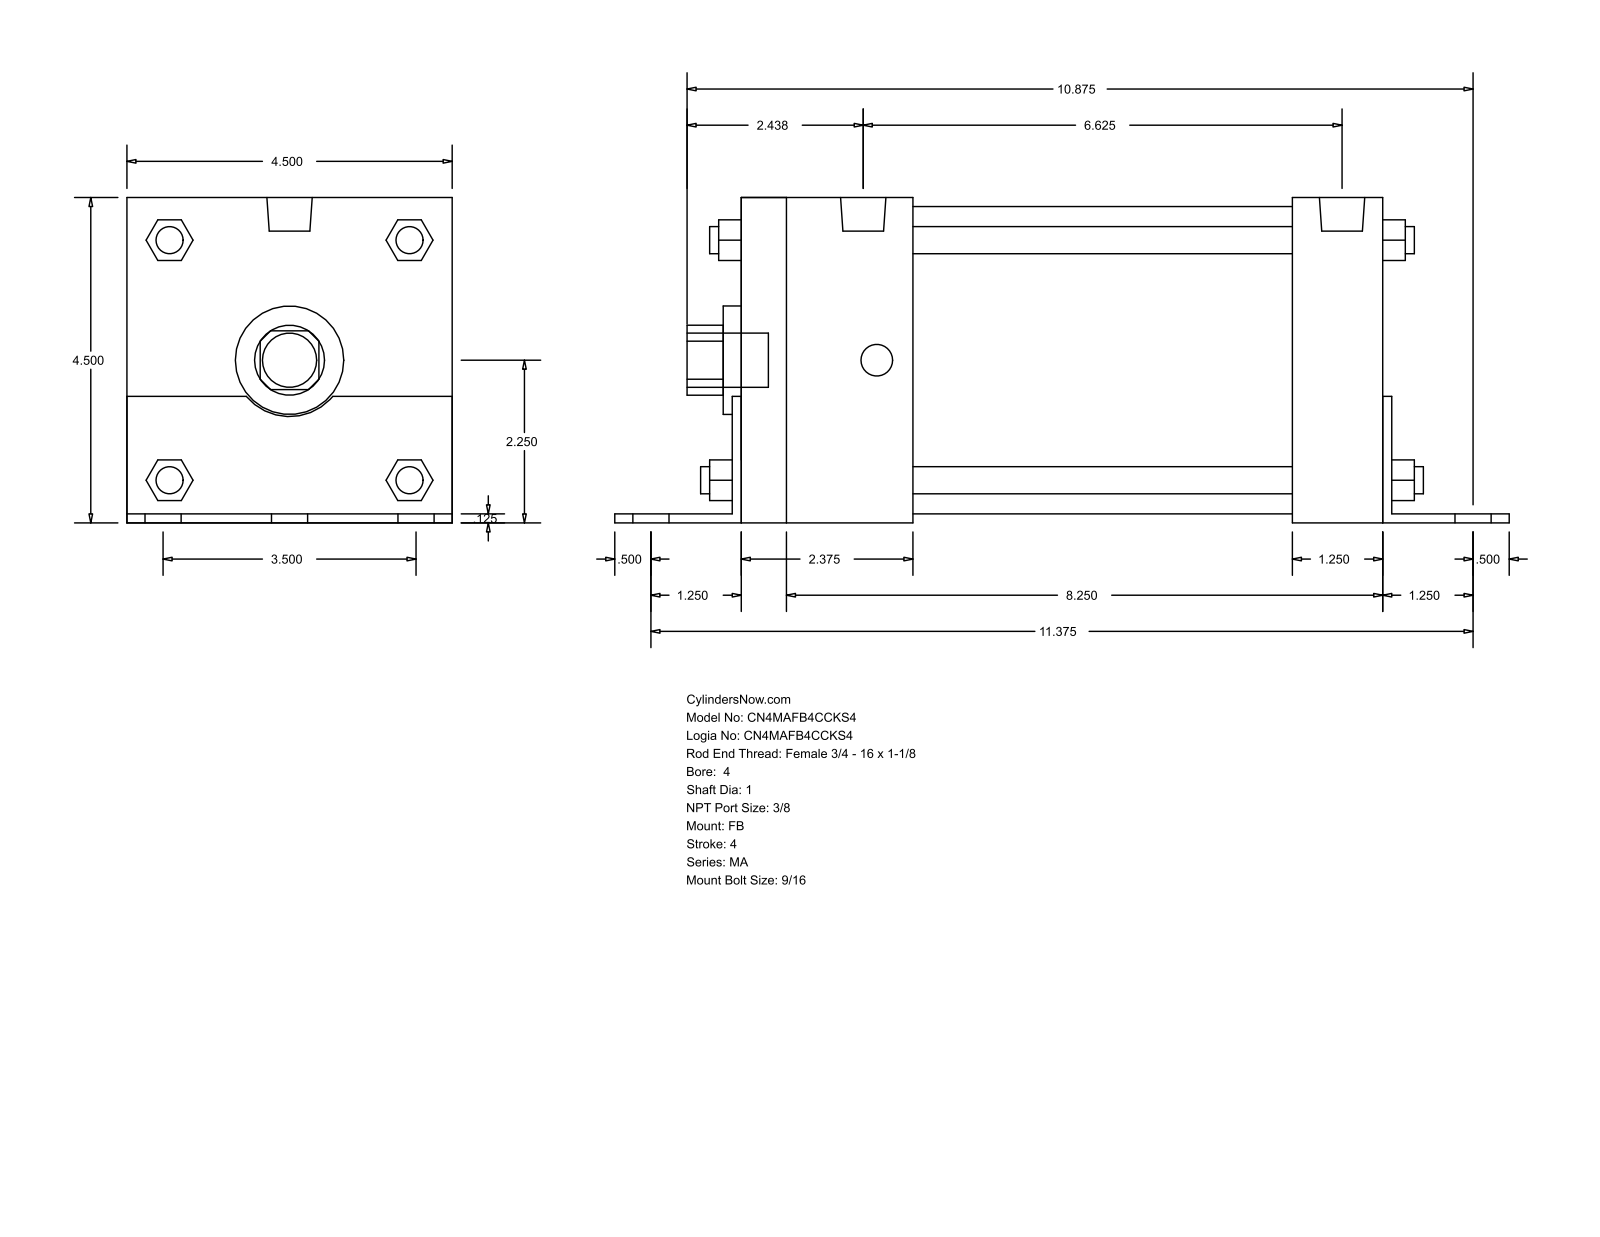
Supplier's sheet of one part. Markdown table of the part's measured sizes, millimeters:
| quantity | value |
| --- | --- |
| part name | MA_FB__0400_1 |
| STEP written by | GSSL Pune (CONFIG_CONTROL_DESIGN) |
| units | millimeters |
| bodies | 0 solids, 140 faces (105 planar, 35 cylindrical, 0 other) |
| overall size | 314.32 × 114.35 × 114.3 |
| round holes (diameter × count) | 25.4 × 1, 38.1 × 1, 107.95 × 1 |
| round bosses / shafts (diameter × count) | 14.29 × 6, 11.11 × 4, 9.53 × 4, 15.93 × 2, 19.05 × 1 |
| partial cylindrical surfaces (radius × count) | 12.29 × 1, 19.81 × 1 |
| main face-to-face distances | 114.3, 3.17, 114.35, 3.12, 111.18, 225.42, 3.18, 231.77, 228.6, 228.59 |
